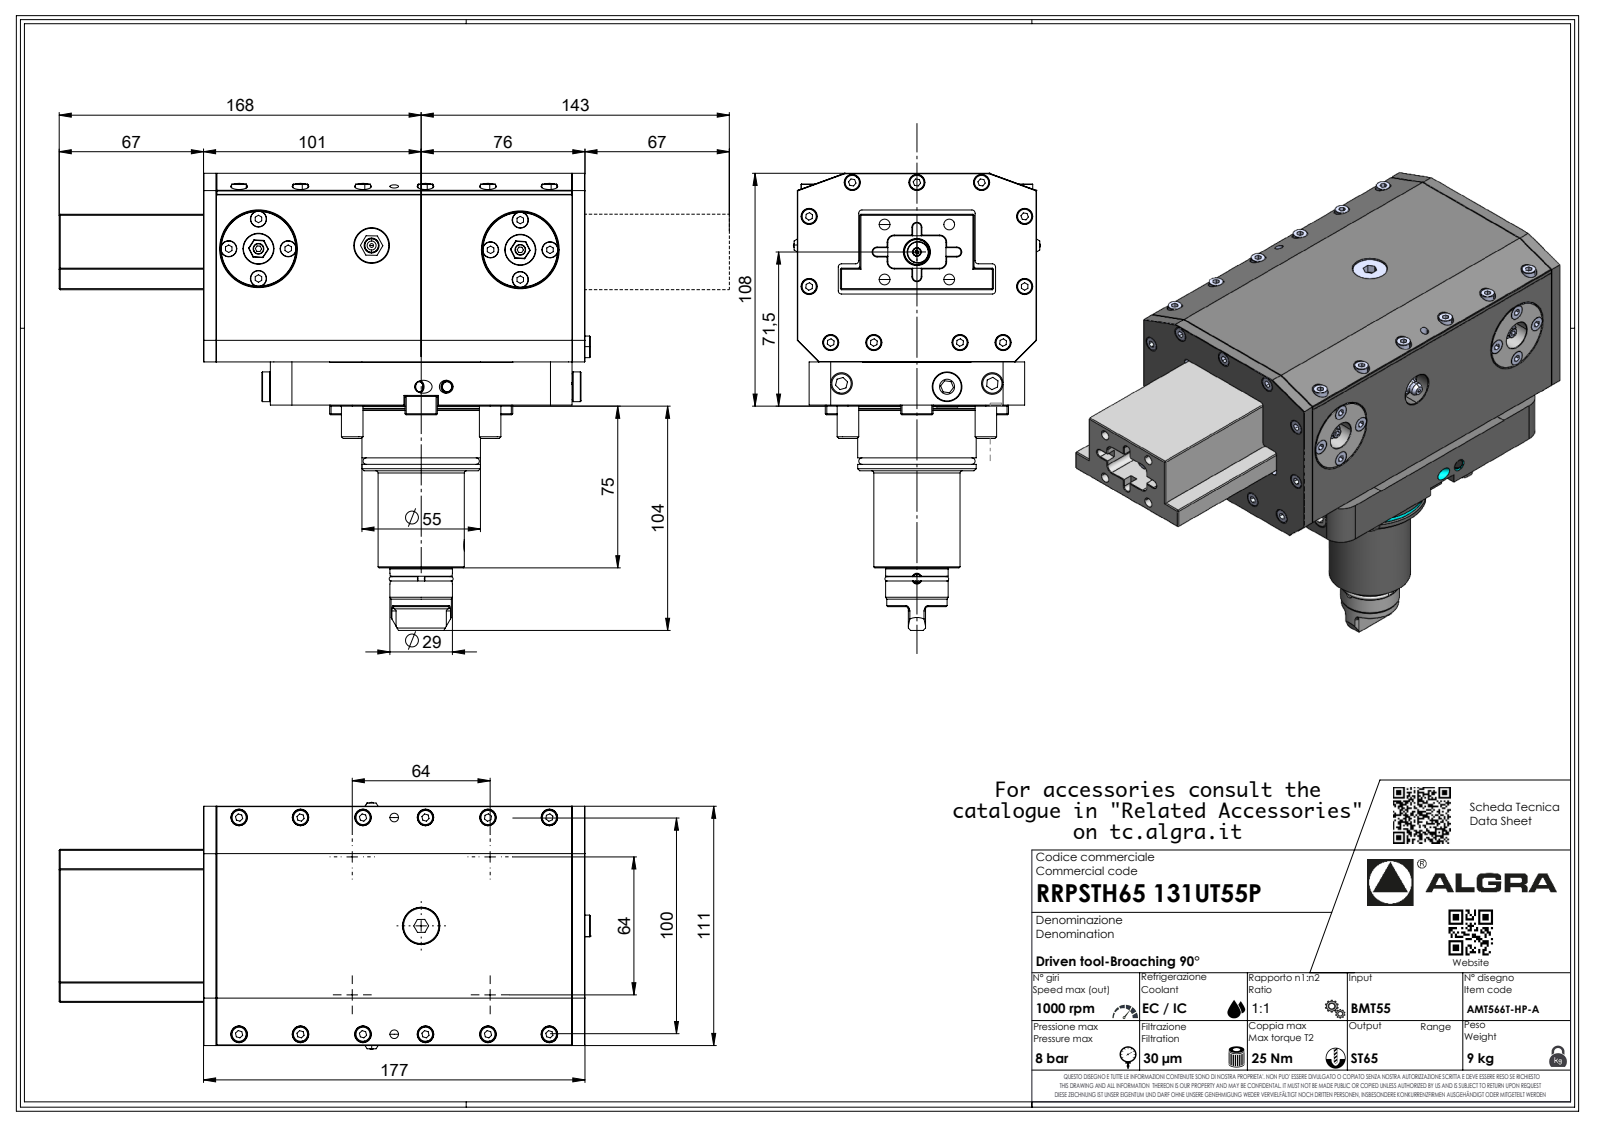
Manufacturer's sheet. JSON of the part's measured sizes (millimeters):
{"part_name": "RRPSTH65131UT55P", "step_written_by": "SolidWorks 2023 (AUTOMOTIVE_DESIGN)", "units": "millimeters", "bodies": {"solids": 1, "faces": 773, "planar": 507, "cylindrical": 117, "other": 149}, "overall_size": [246.47, 212, 114.6], "volume_mm3": 2229000, "surface_area_mm2": 144066, "round_holes": [[2.1, 1], [61, 1]], "round_bosses_or_shafts": [[55, 1], [54.6, 1], [50.2, 1], [40, 1], [29, 1], [28, 1], [10, 1], [6.37, 1]], "partial_cylinders_radius": [[2.5, 12], [3.5, 12], [10, 8], [0.33, 7], [0.52, 7], [3.7, 7], [2, 4], [3, 4]], "face_to_face_distances": [111, 87.5, 87.7, 54, 20, 177, 19.8, 107.5, 33.5, 105.5]}
